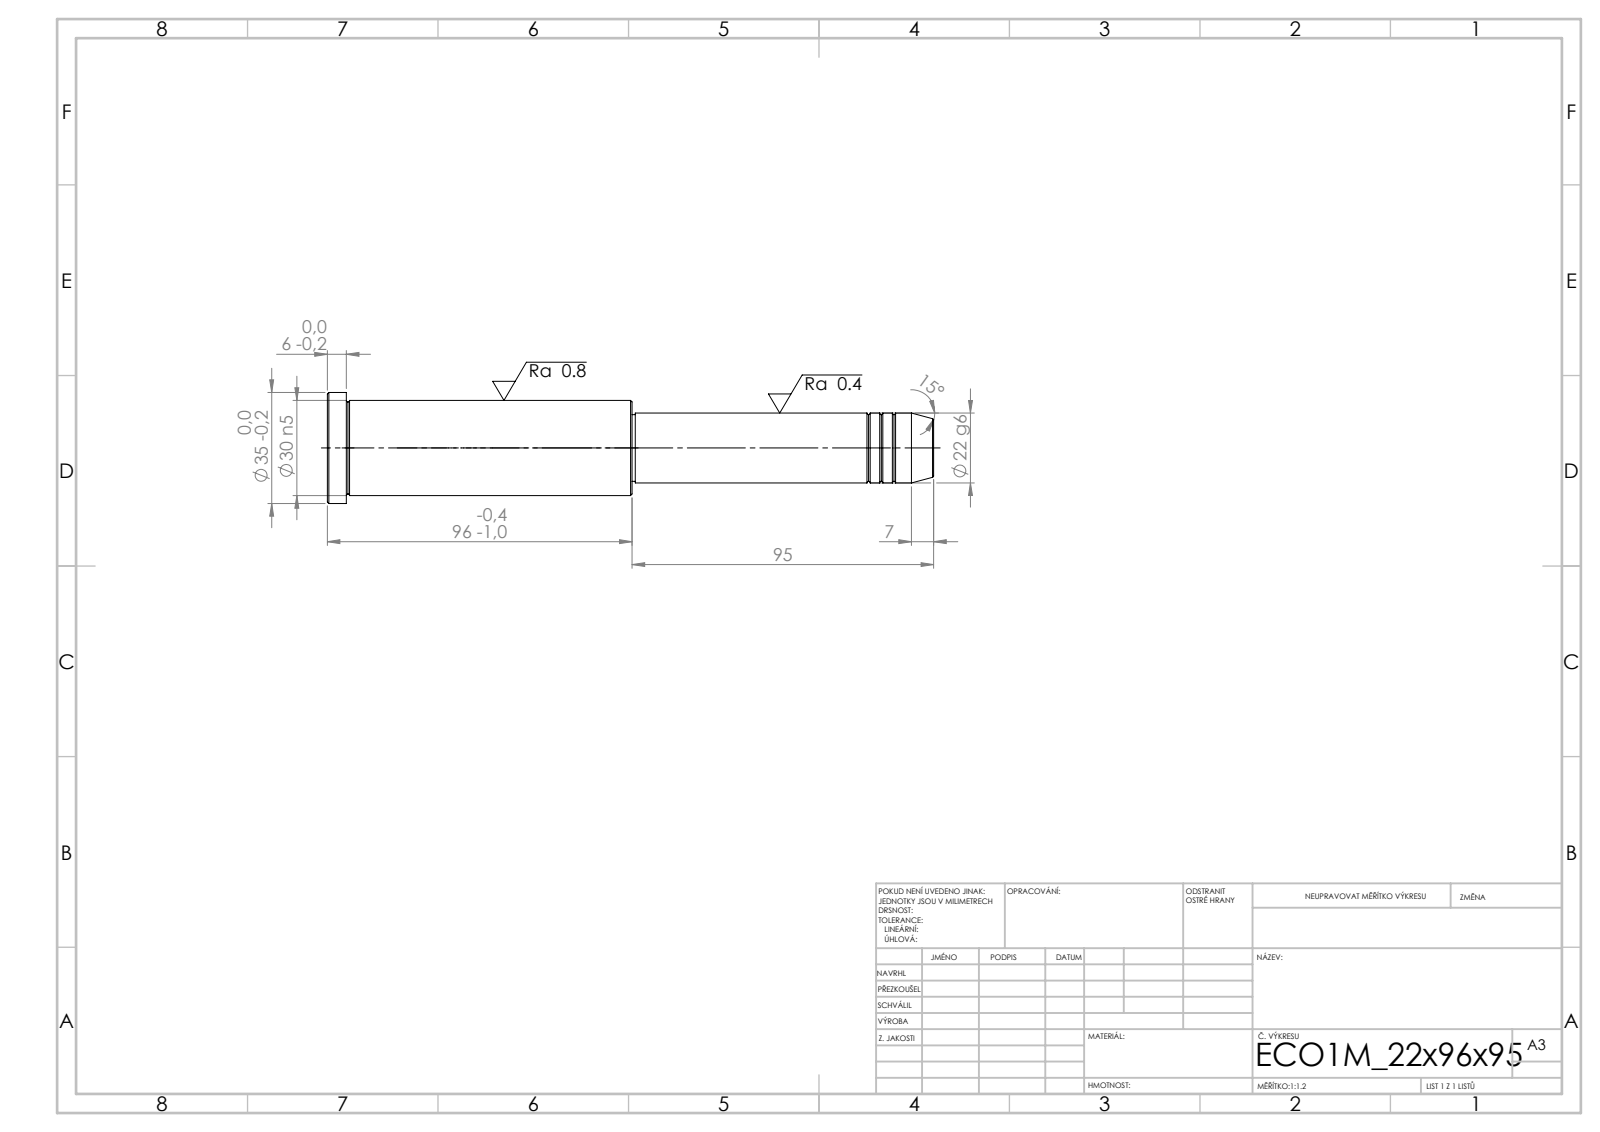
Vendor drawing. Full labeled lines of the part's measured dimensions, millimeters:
STEP written by: SolidWorks 2019 (CONFIG_CONTROL_DESIGN)
Units: millimetres
Bodies: 1 solid, 43 faces (5 planar, 14 cylindrical, 24 other)
Overall size (bounding box): 191 × 35 × 35
Volume: 104 898 mm³ · Surface area: 17 645 mm²
Round bosses / shafts (diameter × count): ⌀35 ×1, ⌀30 ×1, ⌀22 ×1, ⌀21 ×1
Main face-to-face distances: 96, 90, 6, 95, 185, 191, 94, 1, 91, 97
